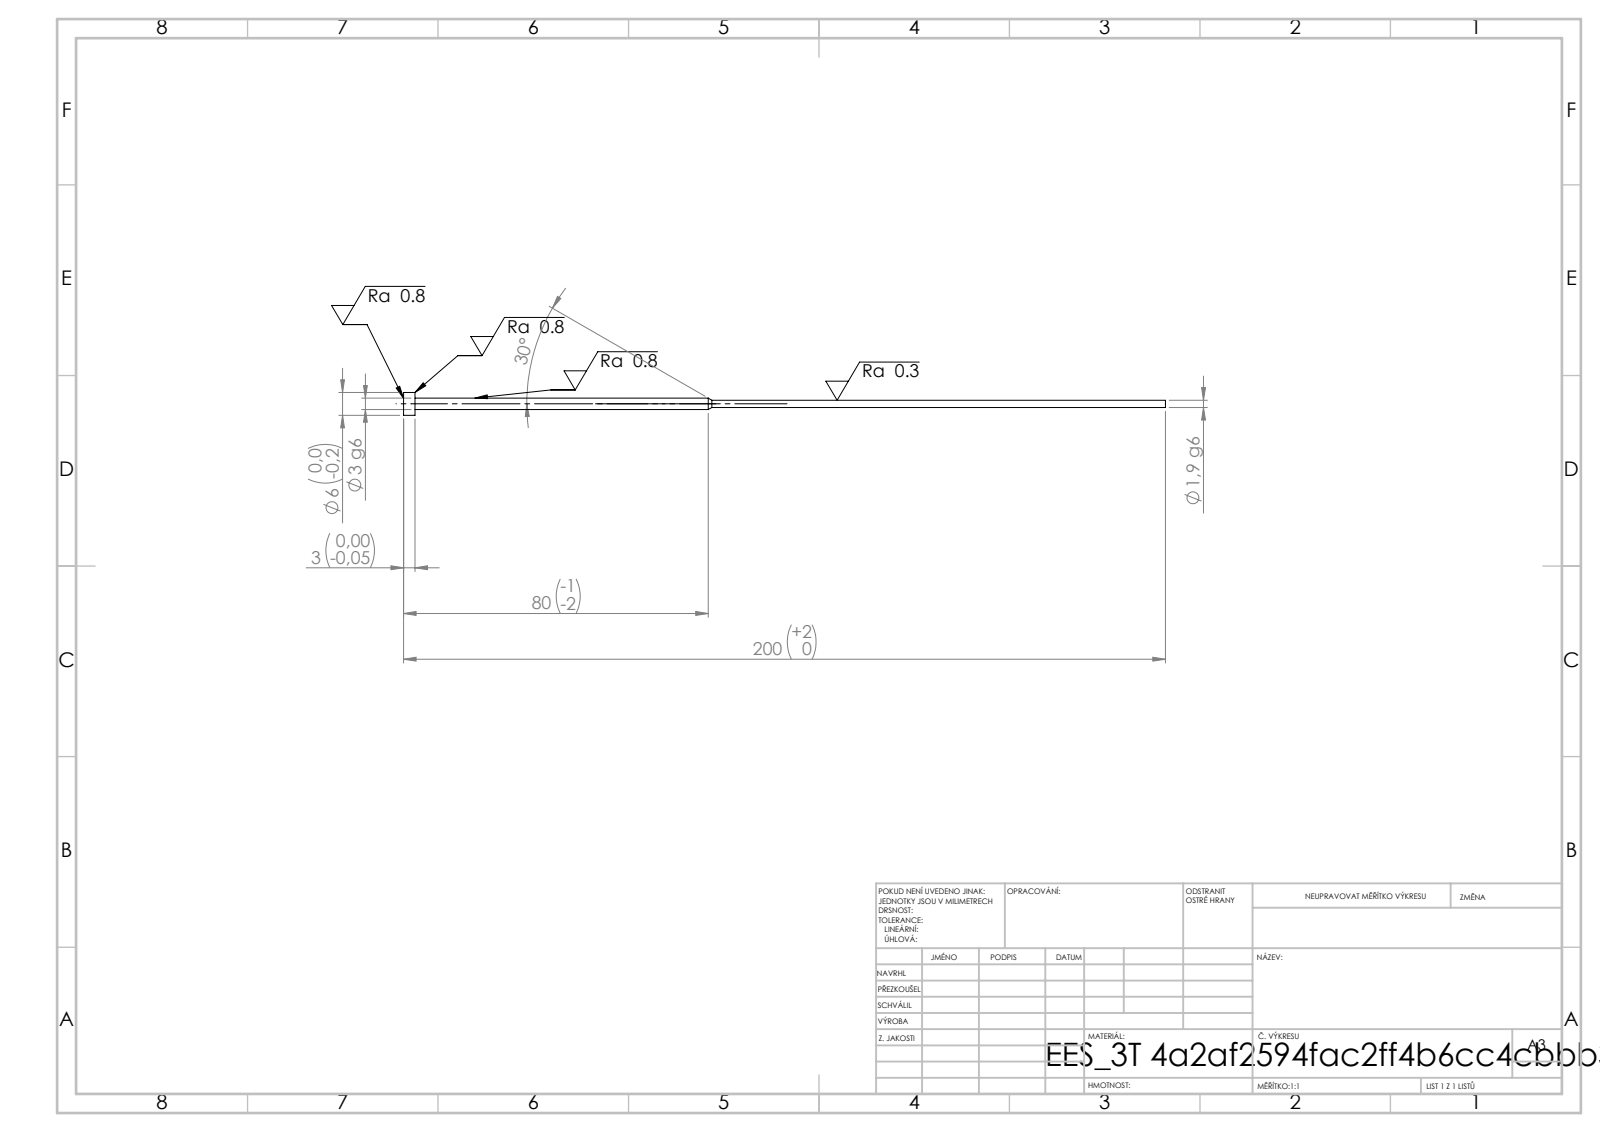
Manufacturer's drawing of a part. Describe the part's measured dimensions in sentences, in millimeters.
Its 3-D file was written by "SolidWorks 2019 (CONFIG_CONTROL_DESIGN)". It is 1 solid with 11 faces: 3 planar, 6 cylindrical and 2 other. Overall it measures 200 by 6 by 6 millimeters. Its volume is 971 cubic millimeters and its surface area 1 554 square millimeters. Round bosses or shafts: 1 of diameter 6, 1 of diameter 3, 1 of diameter 1.9. The main face-to-face distances are 3, 197, 200.
